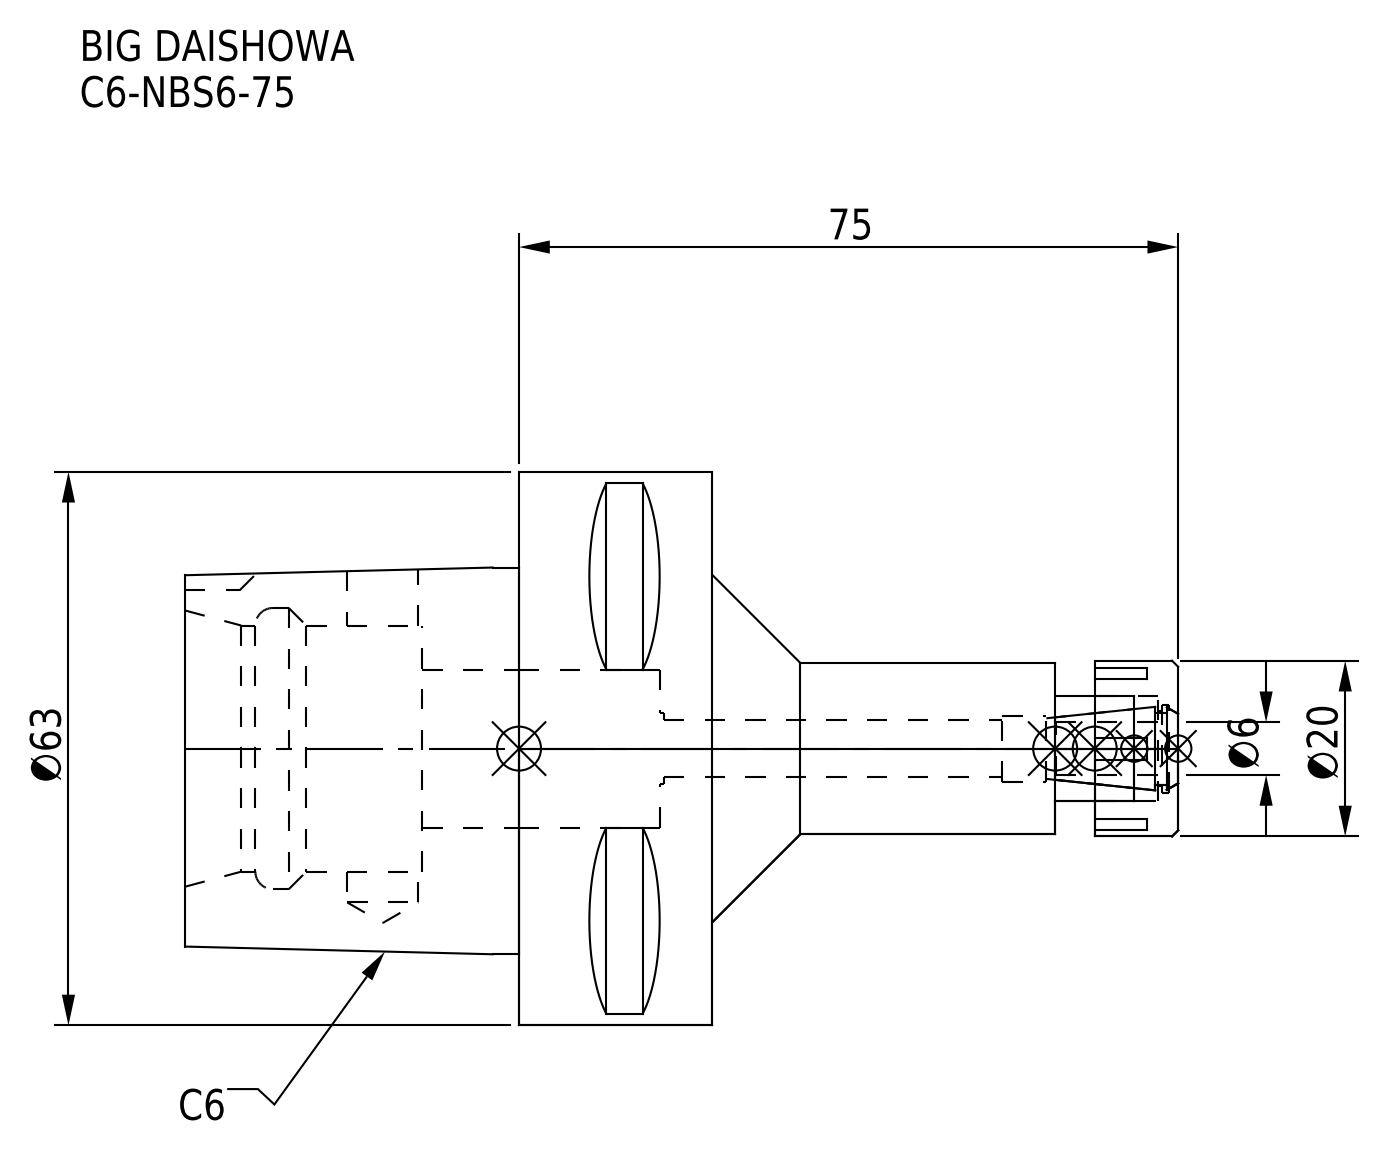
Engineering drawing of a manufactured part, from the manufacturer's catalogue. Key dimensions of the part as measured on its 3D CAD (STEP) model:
Part name (STEP PRODUCT): C6-NBS6-75-060_ASM.stp; DXF_TEMP_ASSY_ASM_4_ASM.stp; C6-NBS6-75.stp; NBN6_1.stp (+3 more)
STEP written by: SolidWorks 2019 (CONFIG_CONTROL_DESIGN)
Units: millimetres
Bodies: 2 solids, 112 faces (61 planar, 33 cylindrical, 18 other)
Overall size (bounding box): 113 × 63 × 63
Volume: 113 234 mm³ · Surface area: 25 294 mm²
Round holes (diameter × count): ⌀6.4 ×1, ⌀7.5 ×1, ⌀8 ×1, ⌀8.1 ×1, ⌀8.5 ×1, ⌀10 ×1, ⌀12 ×1, ⌀18 ×1, ⌀28 ×1, ⌀32 ×1
Round bosses / shafts (diameter × count): ⌀63 ×1, ⌀20 ×1, ⌀19.5 ×1
Partial cylindrical surfaces — rounded edges, fillets, slot ends (radius × count): R5 ×1
Main face-to-face distances: 22, 27, 38, 60, 33, 11, 24.89, 54, 55.4, 6
